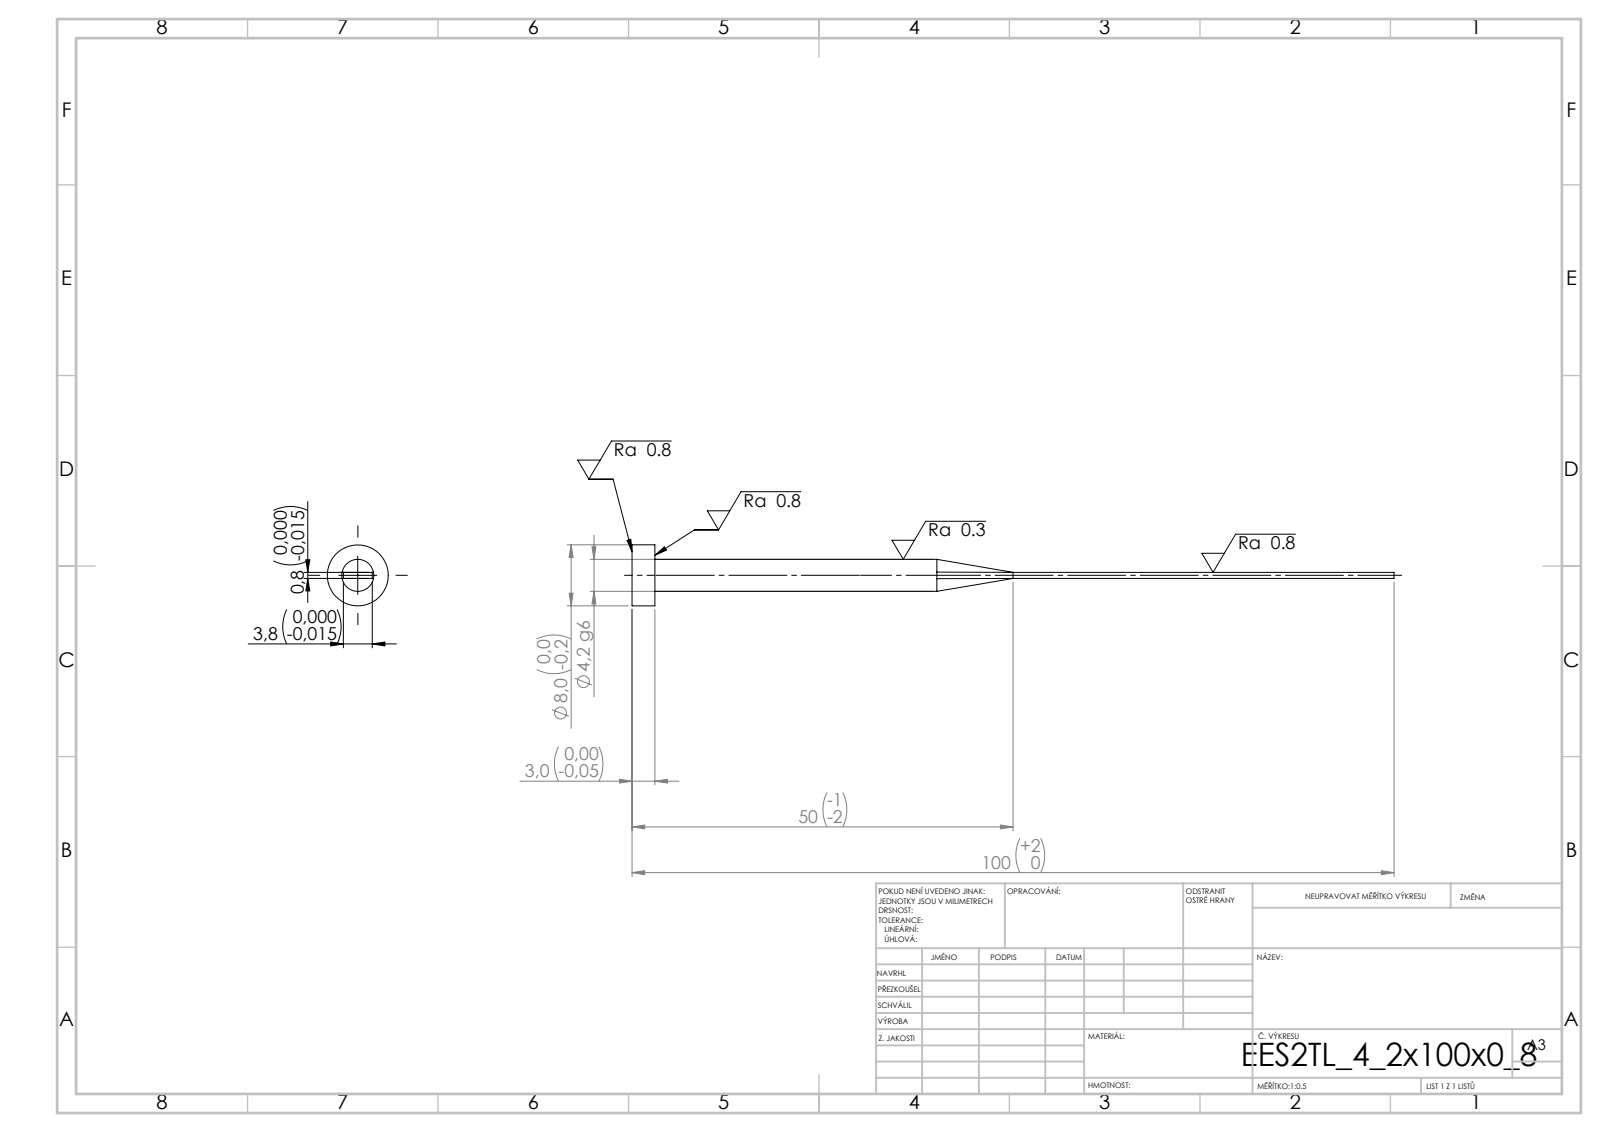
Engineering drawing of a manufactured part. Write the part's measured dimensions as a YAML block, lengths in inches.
step_written_by: "SolidWorks 2019 (CONFIG_CONTROL_DESIGN)"
units: inches
bodies: {solids: 1, faces: 15, planar: 7, cylindrical: 4, other: 4}
overall_size: [3.937, 0.315, 0.315]
volume: 0.055
surface_area: 1.893
round_bosses_or_shafts:
  - {diameter: 0.315, count: 1}
  - {diameter: 0.165, count: 1}
face_to_face_distances: [0.031, 0.15, 0.118, 3.937, 3.819]
